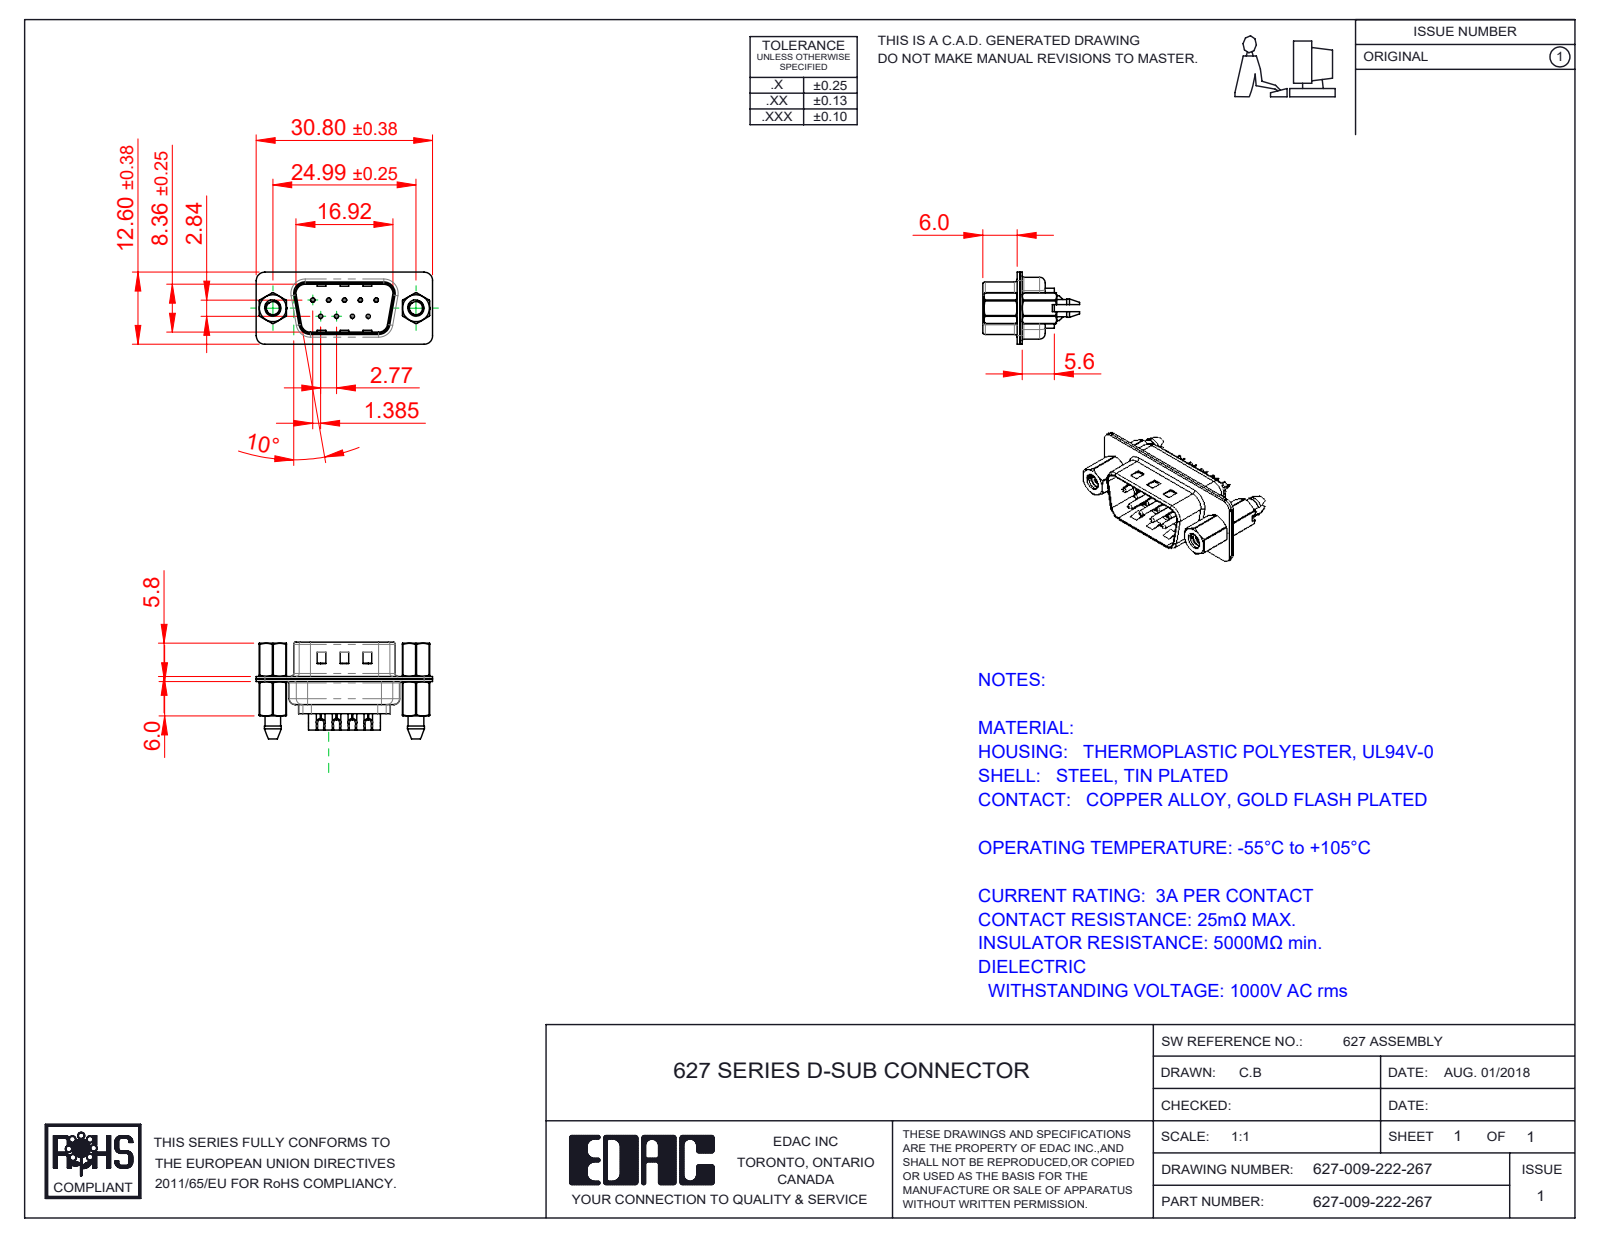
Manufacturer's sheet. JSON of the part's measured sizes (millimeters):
{"part_name": "627 Shell Front_09 Contacts; 627 Contact Row 1_22L; 627 4-40 Hex Standoff; 627-009-222-267 (+4 more)", "step_written_by": "SolidWorks 2020 (CONFIG_CONTROL_DESIGN)", "units": "millimeters", "bodies": {"solids": 16, "faces": 1080, "planar": 287, "cylindrical": 494, "other": 299}, "overall_size": [30.8, 16.9, 12.6], "volume_mm3": 1642, "surface_area_mm2": 4727, "round_holes": [[0.35, 9], [1.1, 9], [1.6, 9], [2.26, 2], [2.29, 2], [4, 2], [4.8, 2]], "round_bosses_or_shafts": [[2, 9], [1.5, 9], [0.75, 9], [4.9, 2], [2.79, 2]], "partial_cylinders_radius": [[1.5, 20], [2, 12], [1.6, 10], [0.5, 8], [1, 6], [0.25, 4], [0.6, 4], [0.65, 4]], "face_to_face_distances": [0.45, 0.4, 0.9, 0.82, 9.58, 1.4, 4.76, 8.76, 6.5, 0.5], "hole_center_spacings": [3.16, 2.77, 5.54, 5.03, 5.04, 8.31, 7.48, 7.49]}
